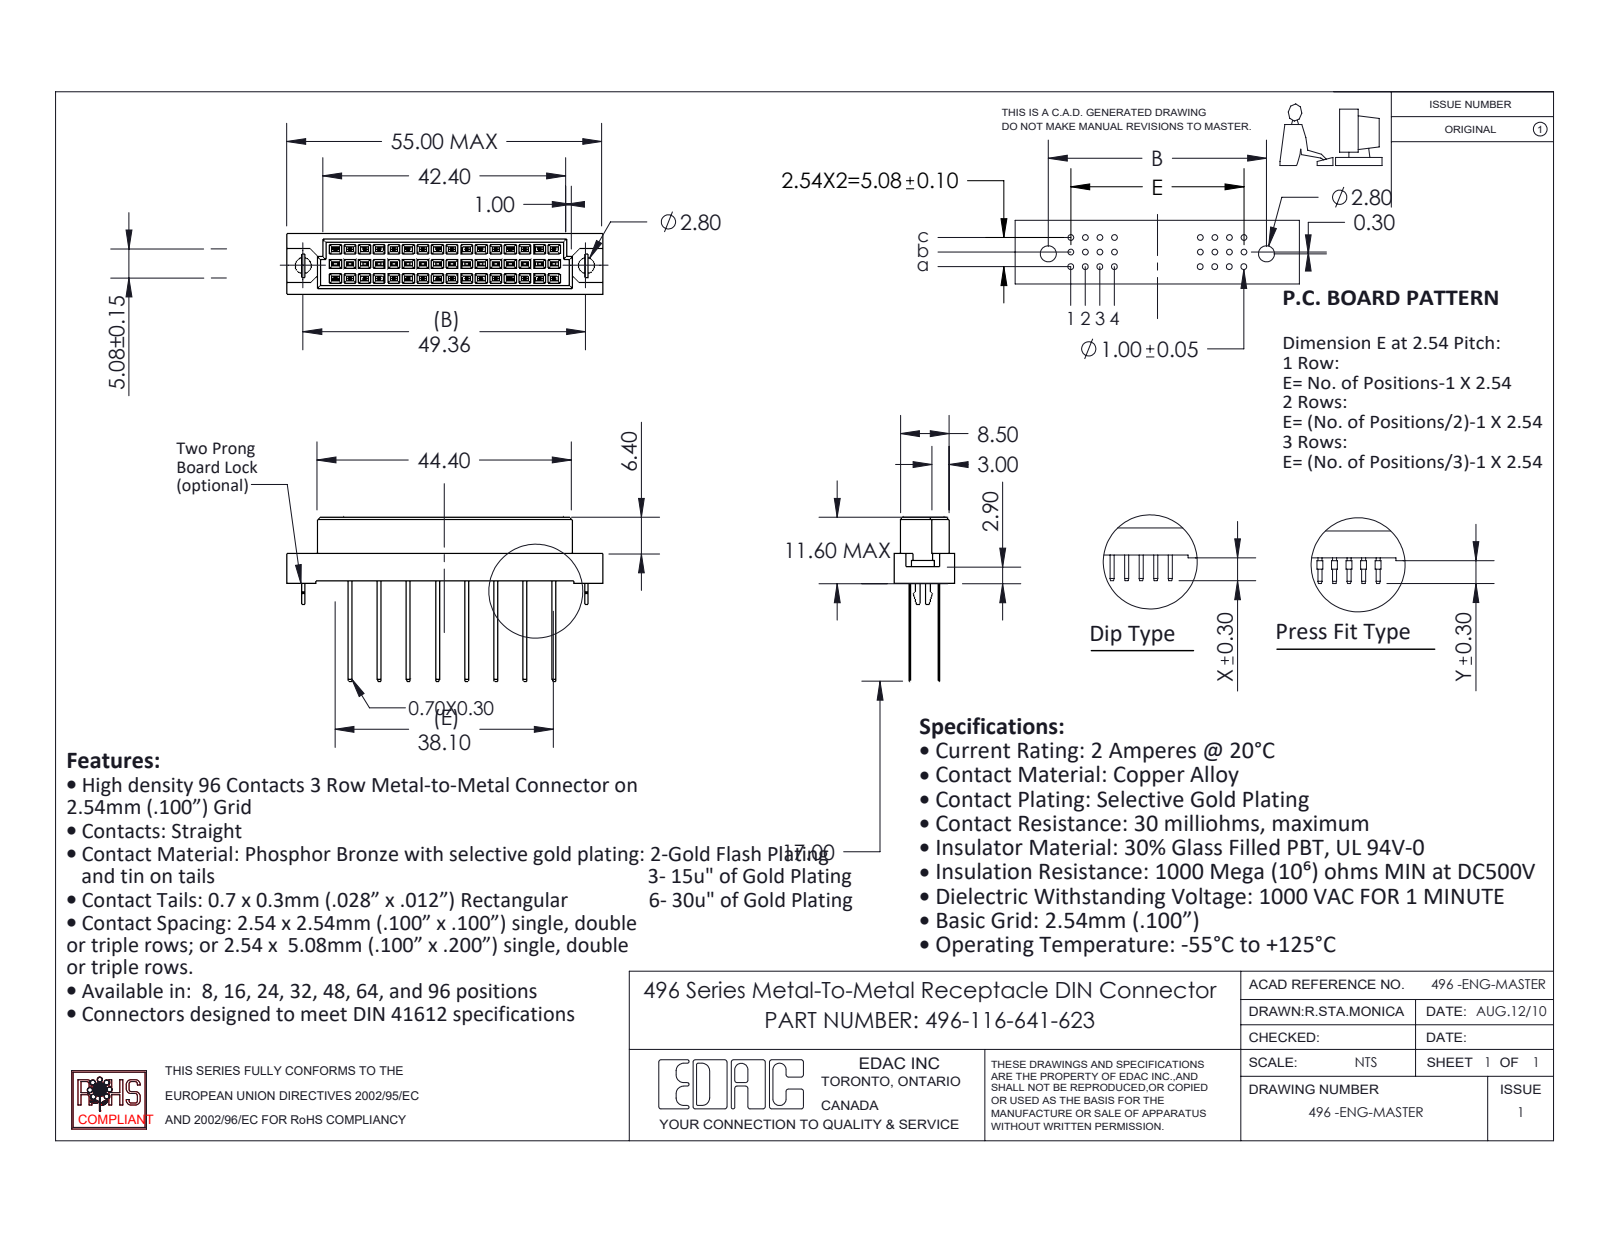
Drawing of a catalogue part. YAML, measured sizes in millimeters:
part_name: "496-116-641-623; 496 Part_48; 496-290_41; 496 Bore-lock"
step_written_by: "SolidWorks 2020 (CONFIG_CONTROL_DESIGN)"
units: millimeters
bodies: {solids: 19, faces: 862, planar: 856, cylindrical: 6, other: 0}
overall_size: [55, 28.6, 10.6]
volume: 4684
surface_area: 5017
round_holes:
  - {diameter: 2.8, count: 2}
partial_cylinders:
  - {radius: 0.53, count: 1}
face_to_face_distances: [5.08, 2.54, 1.05, 9.55, 0.81, 1.56, 1.86, 2.61, 2.91, 7.69]
hole_center_spacings: [49.36]
